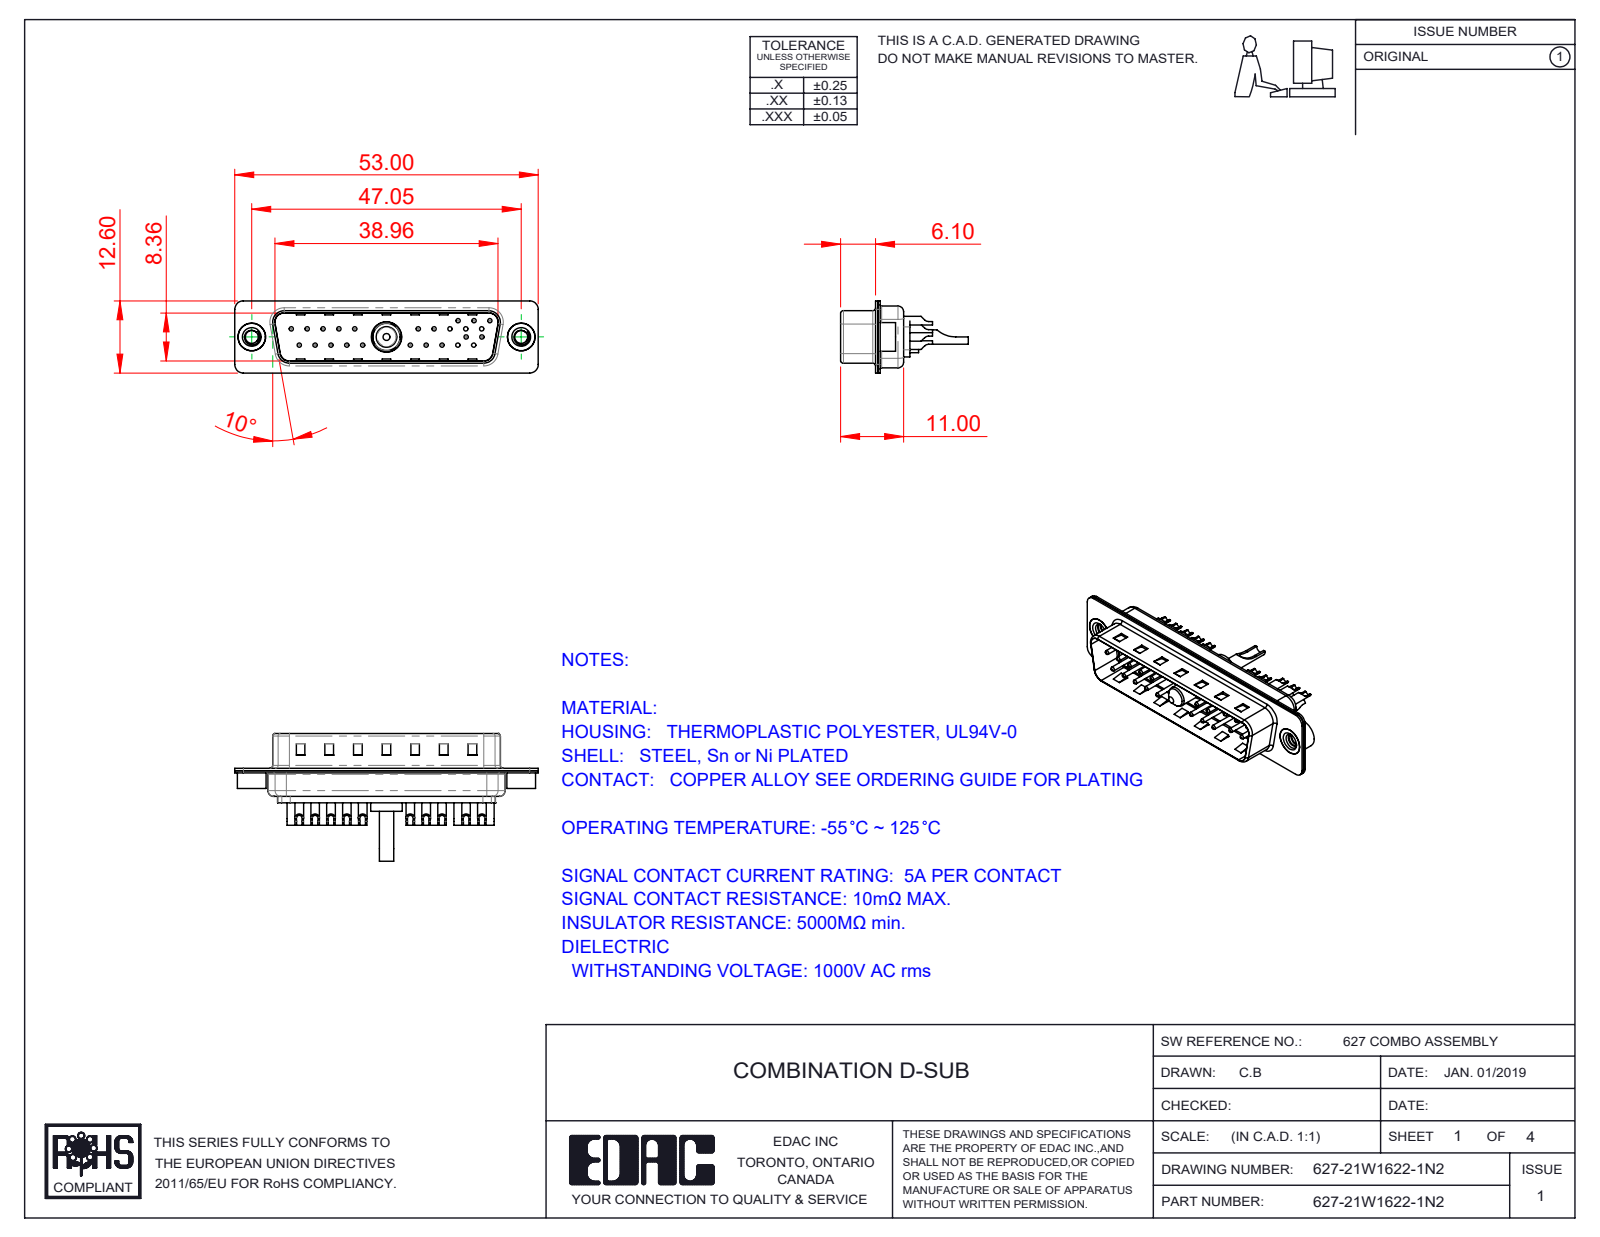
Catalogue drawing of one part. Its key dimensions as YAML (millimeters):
part_name: "627Combo Housing_21W1; 627Combo Shell Front_25 Contacts; Power Pin_10A SC; 627Combo Threaded Rivet_2 (+4 more)"
step_written_by: "SolidWorks 2016 (CONFIG_CONTROL_DESIGN)"
units: millimeters
bodies: {solids: 27, faces: 1161, planar: 363, cylindrical: 479, other: 319}
overall_size: [53, 22.3, 12.6]
volume: 2816
surface_area: 7035
round_holes:
  - {diameter: 0.75, count: 20}
  - {diameter: 1, count: 20}
  - {diameter: 1.6, count: 20}
  - {diameter: 2, count: 20}
  - {diameter: 2.26, count: 2}
  - {diameter: 4, count: 2}
  - {diameter: 4.8, count: 2}
  - {diameter: 1.7, count: 1}
  - {diameter: 4.85, count: 1}
  - {diameter: 5.3, count: 1}
round_bosses_or_shafts:
  - {diameter: 1.5, count: 20}
  - {diameter: 2, count: 5}
  - {diameter: 0.75, count: 5}
  - {diameter: 5, count: 2}
  - {diameter: 4.9, count: 2}
  - {diameter: 5.5, count: 1}
  - {diameter: 5.2, count: 1}
  - {diameter: 4.75, count: 1}
partial_cylinders:
  - {radius: 1.5, count: 16}
  - {radius: 2, count: 12}
  - {radius: 0.5, count: 8}
  - {radius: 1, count: 8}
  - {radius: 1.6, count: 8}
  - {radius: 0.25, count: 4}
  - {radius: 0.6, count: 4}
  - {radius: 0.65, count: 4}
face_to_face_distances: [0.4, 0.82, 9.58, 8.76, 1.5, 5.6, 5.2, 6, 1.22, 9.98]
hole_center_spacings: [3.16, 2.77, 5.54, 5.04, 8.31, 19.39, 20.97, 22.16]
